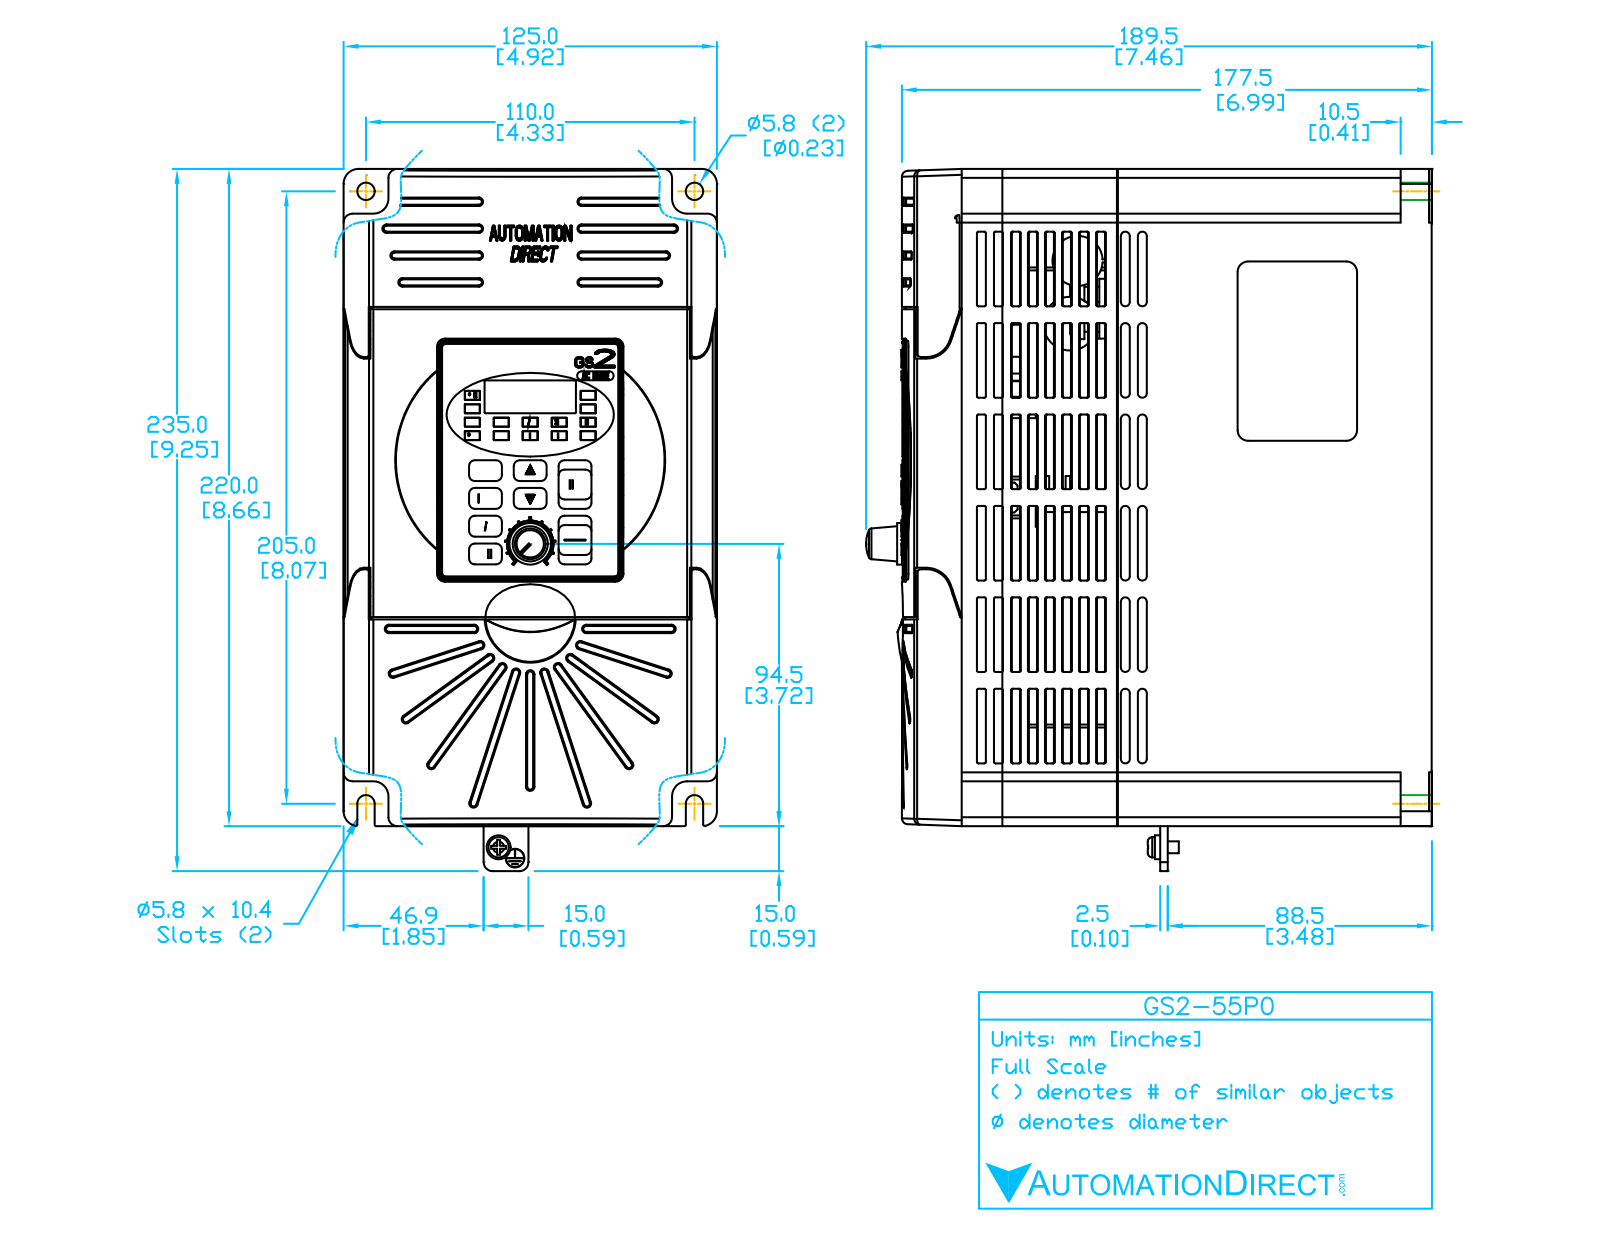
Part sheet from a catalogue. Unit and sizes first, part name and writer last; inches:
Units: inches
Overall size (bounding box): 9.25 × 7.485 × 4.92
Round holes (diameter × count): ⌀0.23 ×2, ⌀3.2 ×1
Round bosses / shafts (diameter × count): ⌀0.545 ×1, ⌀0.258 ×1, ⌀0.15 ×1
Partial cylindrical surfaces — rounded edges, fillets, slot ends (radius × count): R0.06 ×40, R0.04 ×38, R0.125 ×12, R0.2 ×8, R0.019 ×6, R0.064 ×6, R0.25 ×6, R0.1 ×4
Main face-to-face distances: 0.015, 4.905, 4.92, 6.181, 8.645, 4.89, 8.66, 6.17, 0.58, 0.565
Hole centre spacings: 4.33
Volume: 282.9 in³ · Surface area: 350.8 in²
Bodies: 1 solid, 789 faces (355 planar, 218 cylindrical, 216 other)
Part name (STEP PRODUCT): GS2-55P0
STEP written by: SolidWorks 2013 (AUTOMOTIVE_DESIGN)
